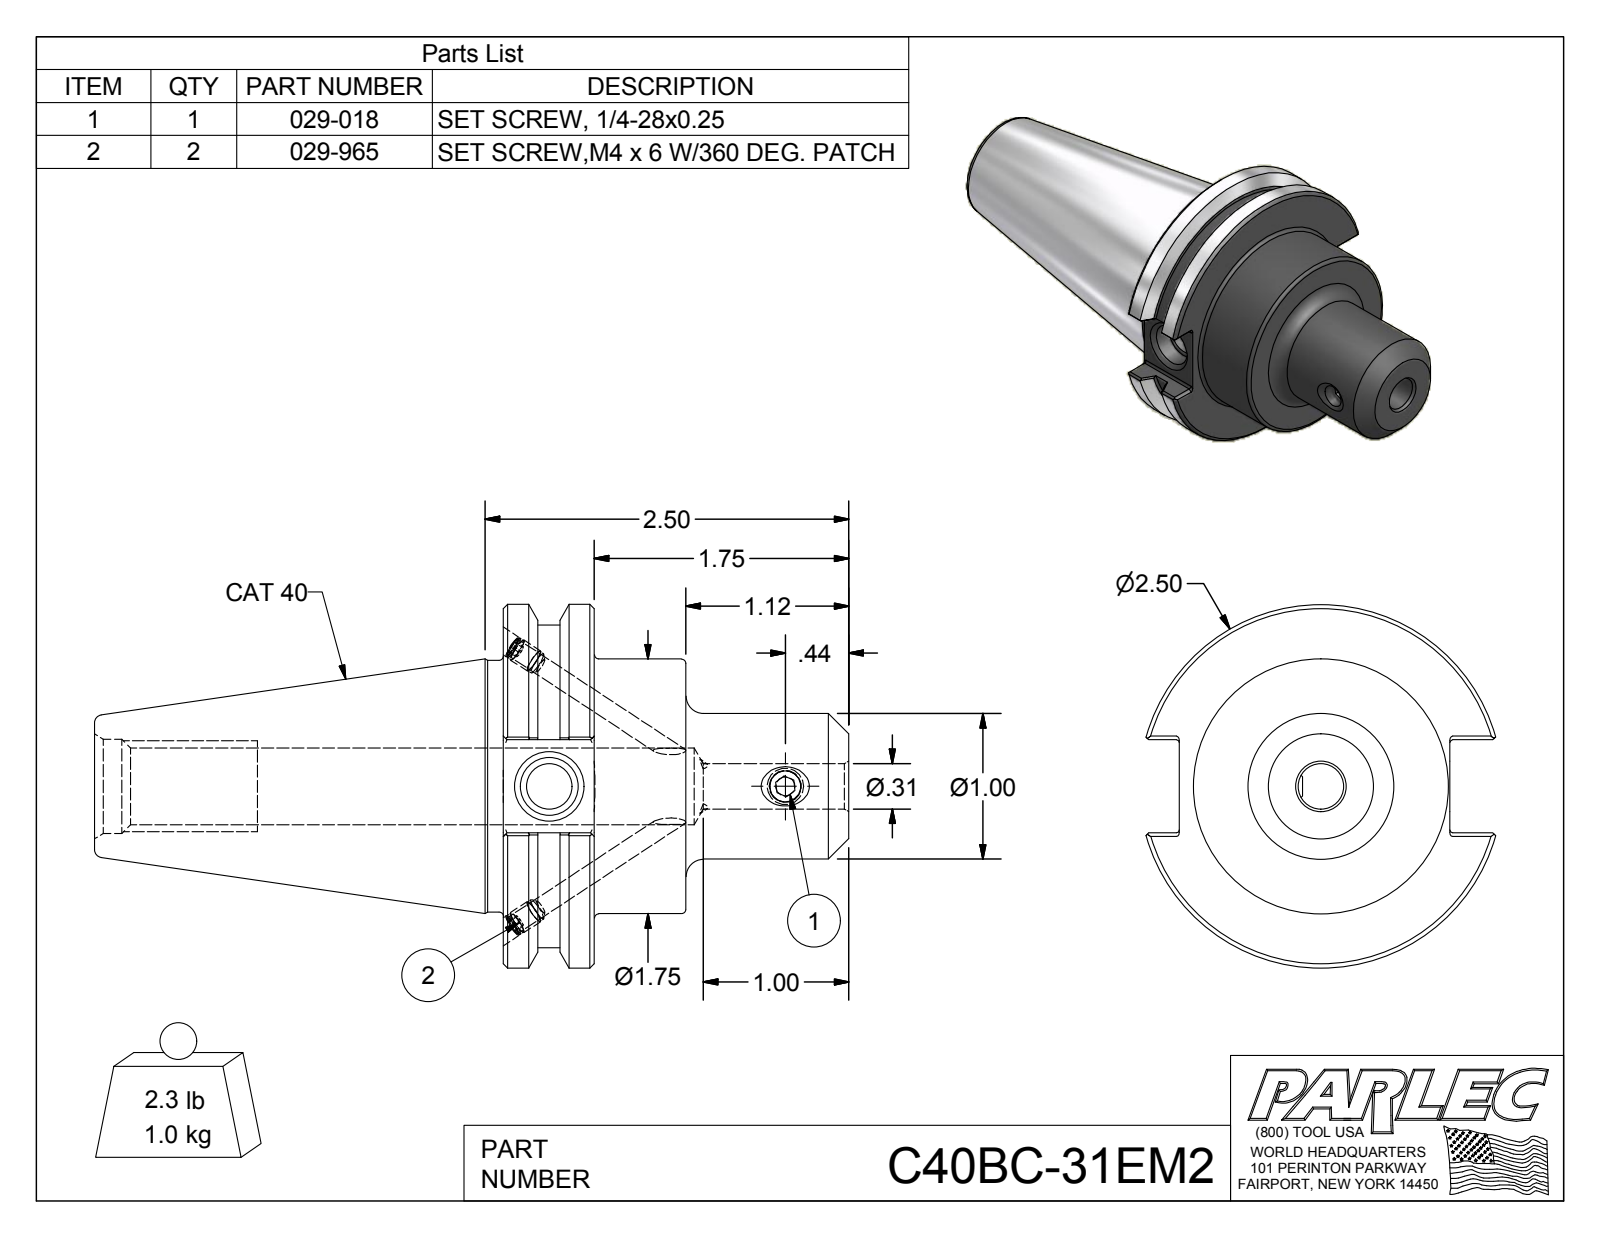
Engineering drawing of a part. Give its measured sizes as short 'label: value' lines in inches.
name: C40BC-31EM2; C40BC-31EM2-1; 029-018; 029-965
written by: Autodesk Inventor 2012 (AUTOMOTIVE_DESIGN)
unit: in
bodies: 4 solids, 142 faces (63 planar, 40 cylindrical, 39 other)
size: 5.187 × 2.5 × 2.406
volume: 8.232 in³; area: 41.97 in²
holes: 2× ⌀0.13, 2× ⌀0.161, 1× ⌀0.211, 1× ⌀0.313, 1× ⌀0.315, 1× ⌀0.399, 1× ⌀0.527, 1× ⌀0.648
bosses: 2× ⌀0.165, 2× ⌀0.157, 1× ⌀2.5, 1× ⌀2.219, 1× ⌀1.75, 1× ⌀1.73, 1× ⌀1, 1× ⌀0.25
rounds: 12× R0.02
face distances: 0.625, 1.255, 0.63, 2.375, 1.75, 1.12, 0.64, 1.86, 2.812, 3.437
hole spacings: 1.623
